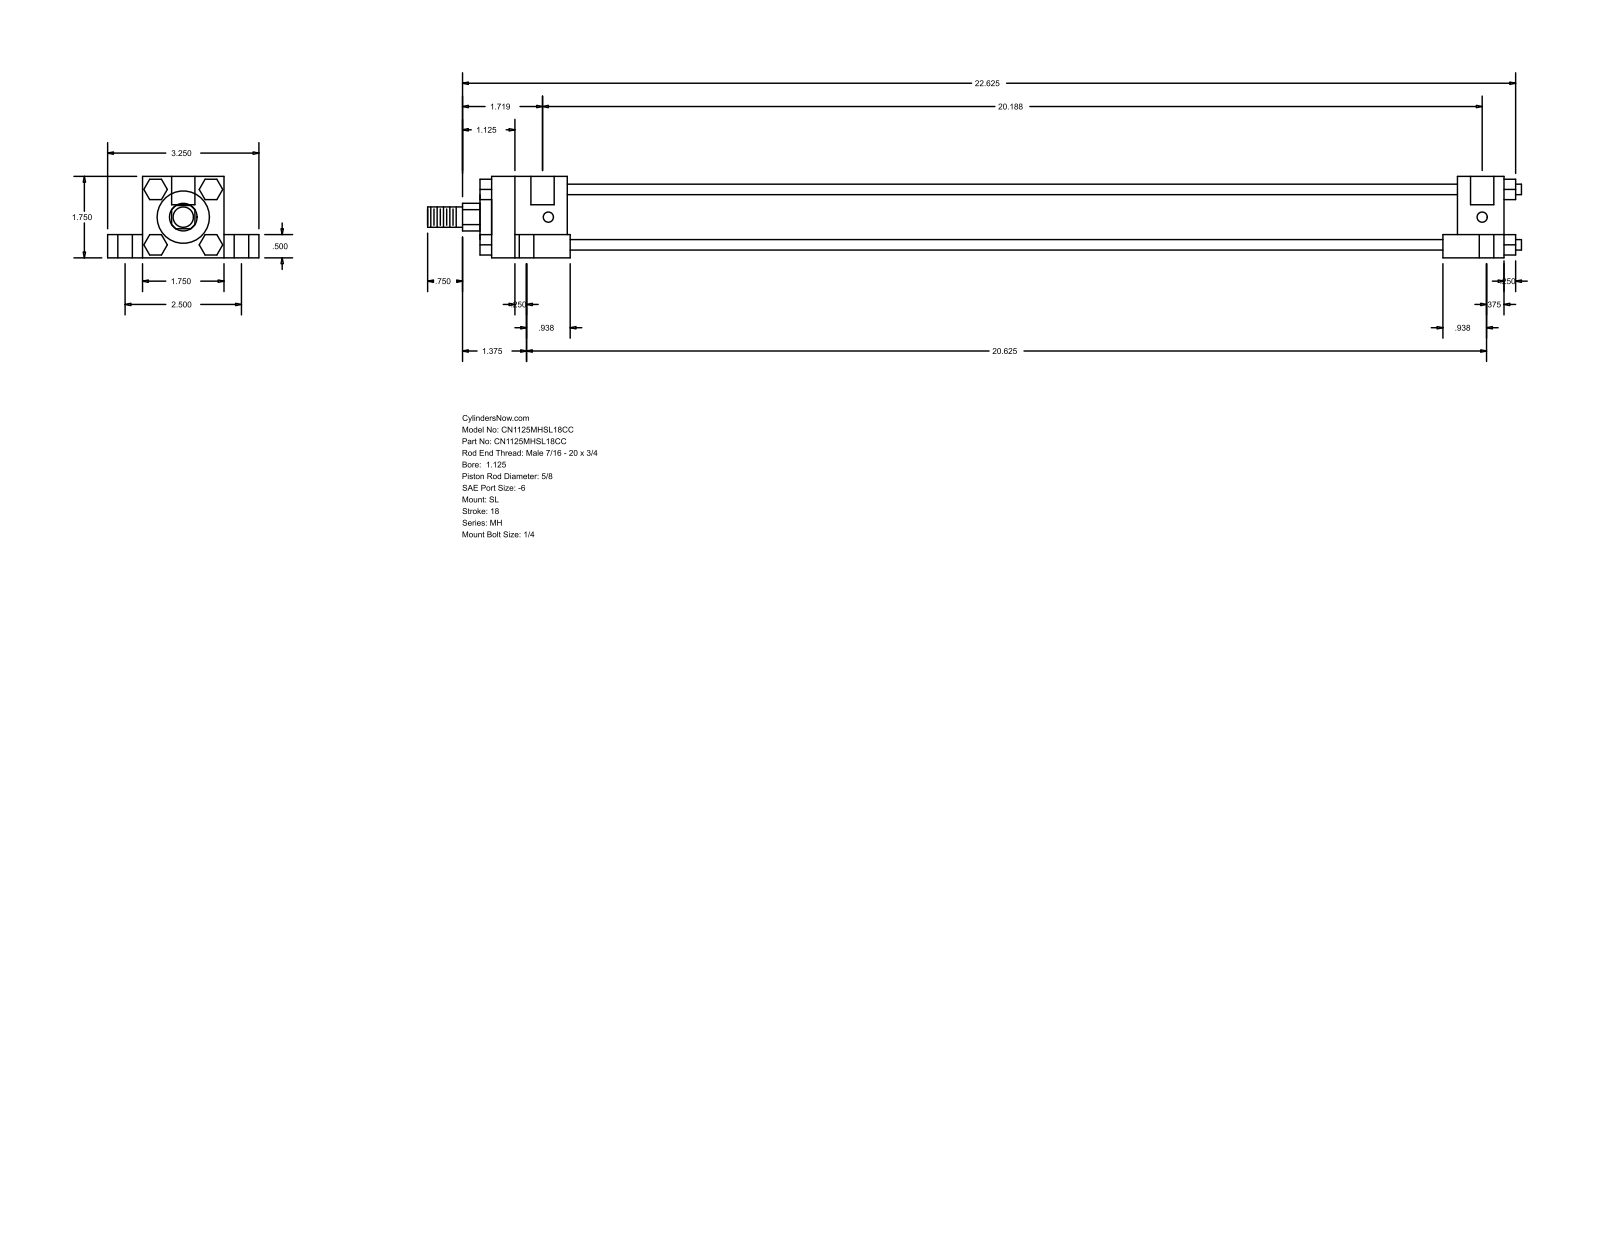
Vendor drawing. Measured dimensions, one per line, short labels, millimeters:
name: MH_SL__0112_0.625
written by: GSSL Pune (CONFIG_CONTROL_DESIGN)
unit: mm
bodies: 0 solids, 150 faces (114 planar, 36 cylindrical, 0 other)
size: 596.9 × 82.55 × 44.45
holes: 4× ⌀5.56, 4× ⌀7.94, 4× ⌀14.29, 2× ⌀12.7
bosses: 4× ⌀5.71, 1× ⌀34.92, 1× ⌀28.57, 1× ⌀15.88, 1× ⌀11.11
rounds: 1× R7.54
face distances: 44.46, 19.04, 12.7, 31.76, 63.5, 11.11, 47.62, 33.34, 506.42, 485.77
hole spacings: 31.84, 32.23, 32.93, 63.5, 509.59, 512.95, 516.12, 519.29
